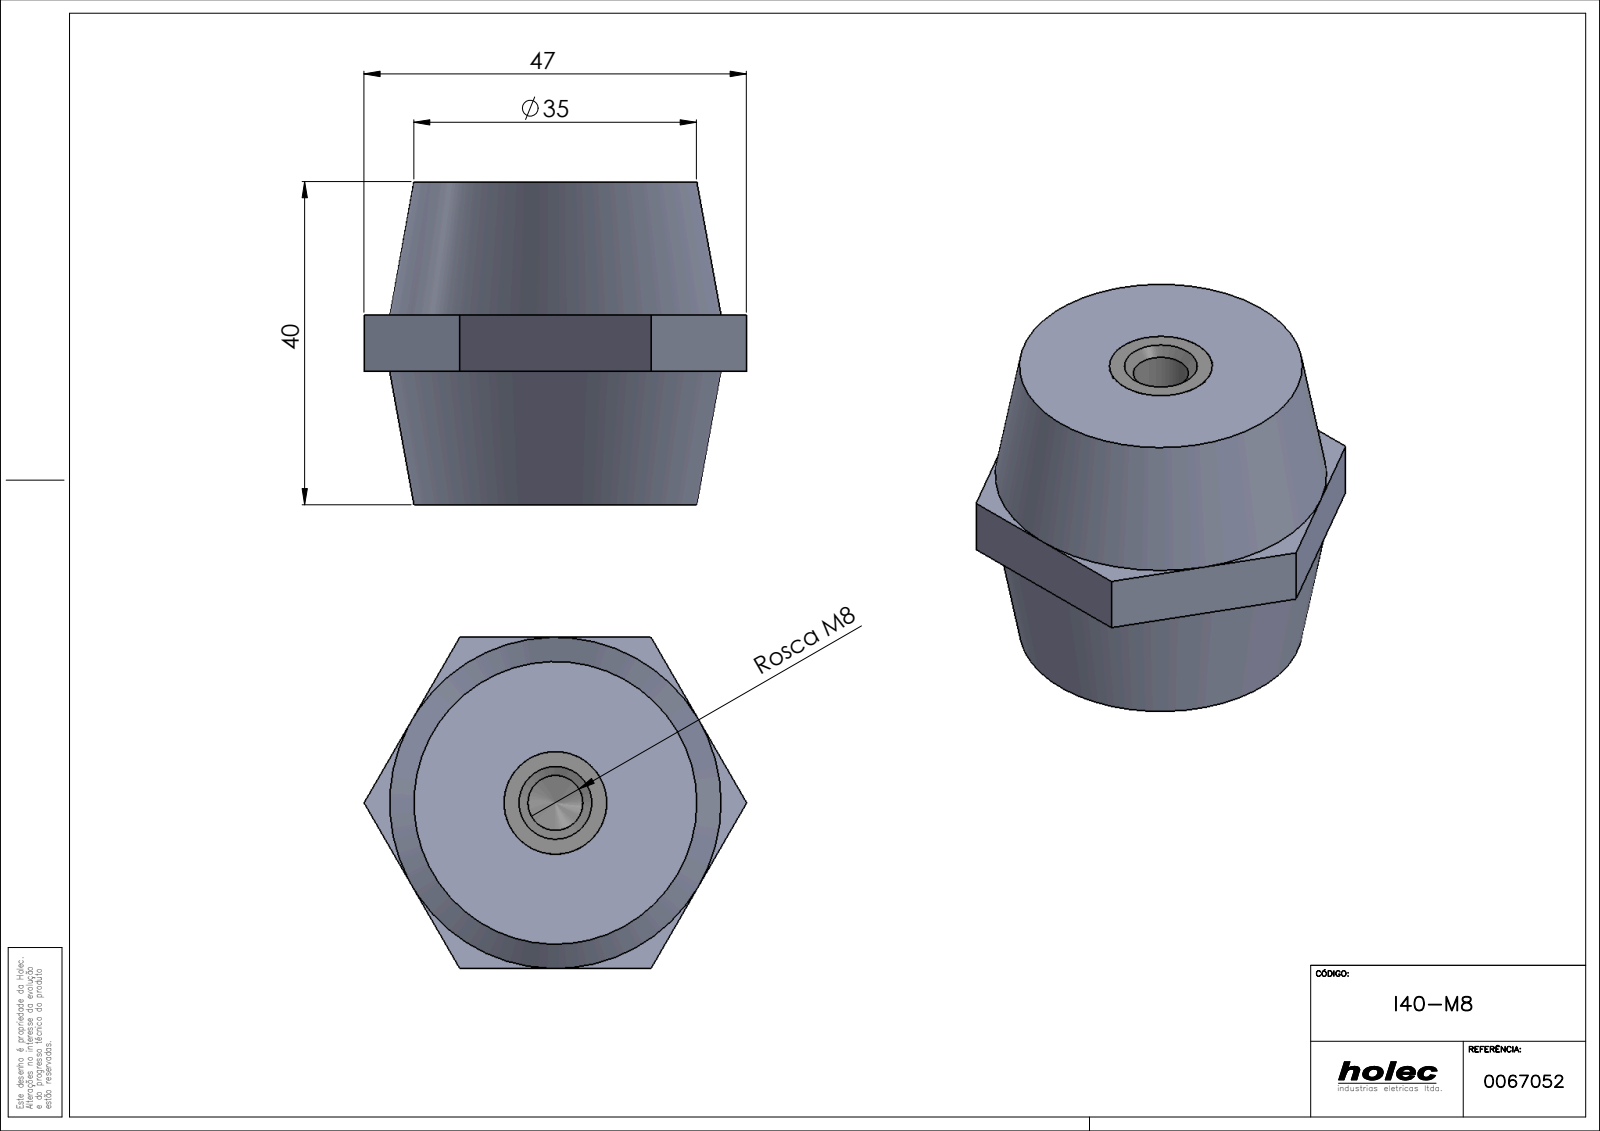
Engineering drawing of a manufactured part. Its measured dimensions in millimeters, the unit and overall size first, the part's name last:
Units: millimetres
Overall size (bounding box): 47.34 × 41 × 40
Round holes (diameter × count): ⌀6.8 ×1, ⌀10 ×1
Main face-to-face distances: 40, 6.5, 12.7, 30.01, 41, 23.5, 10, 30, 6.51, 20.01
Volume: 47 077 mm³ · Surface area: 10 131 mm²
Bodies: 3 solids, 154 faces (82 planar, 12 cylindrical, 60 other)
Part name (STEP PRODUCT): I40-M8; PB1_0001; PB1_0104(PB1_0104_08)
STEP written by: SolidWorks 2017 (AUTOMOTIVE_DESIGN)
